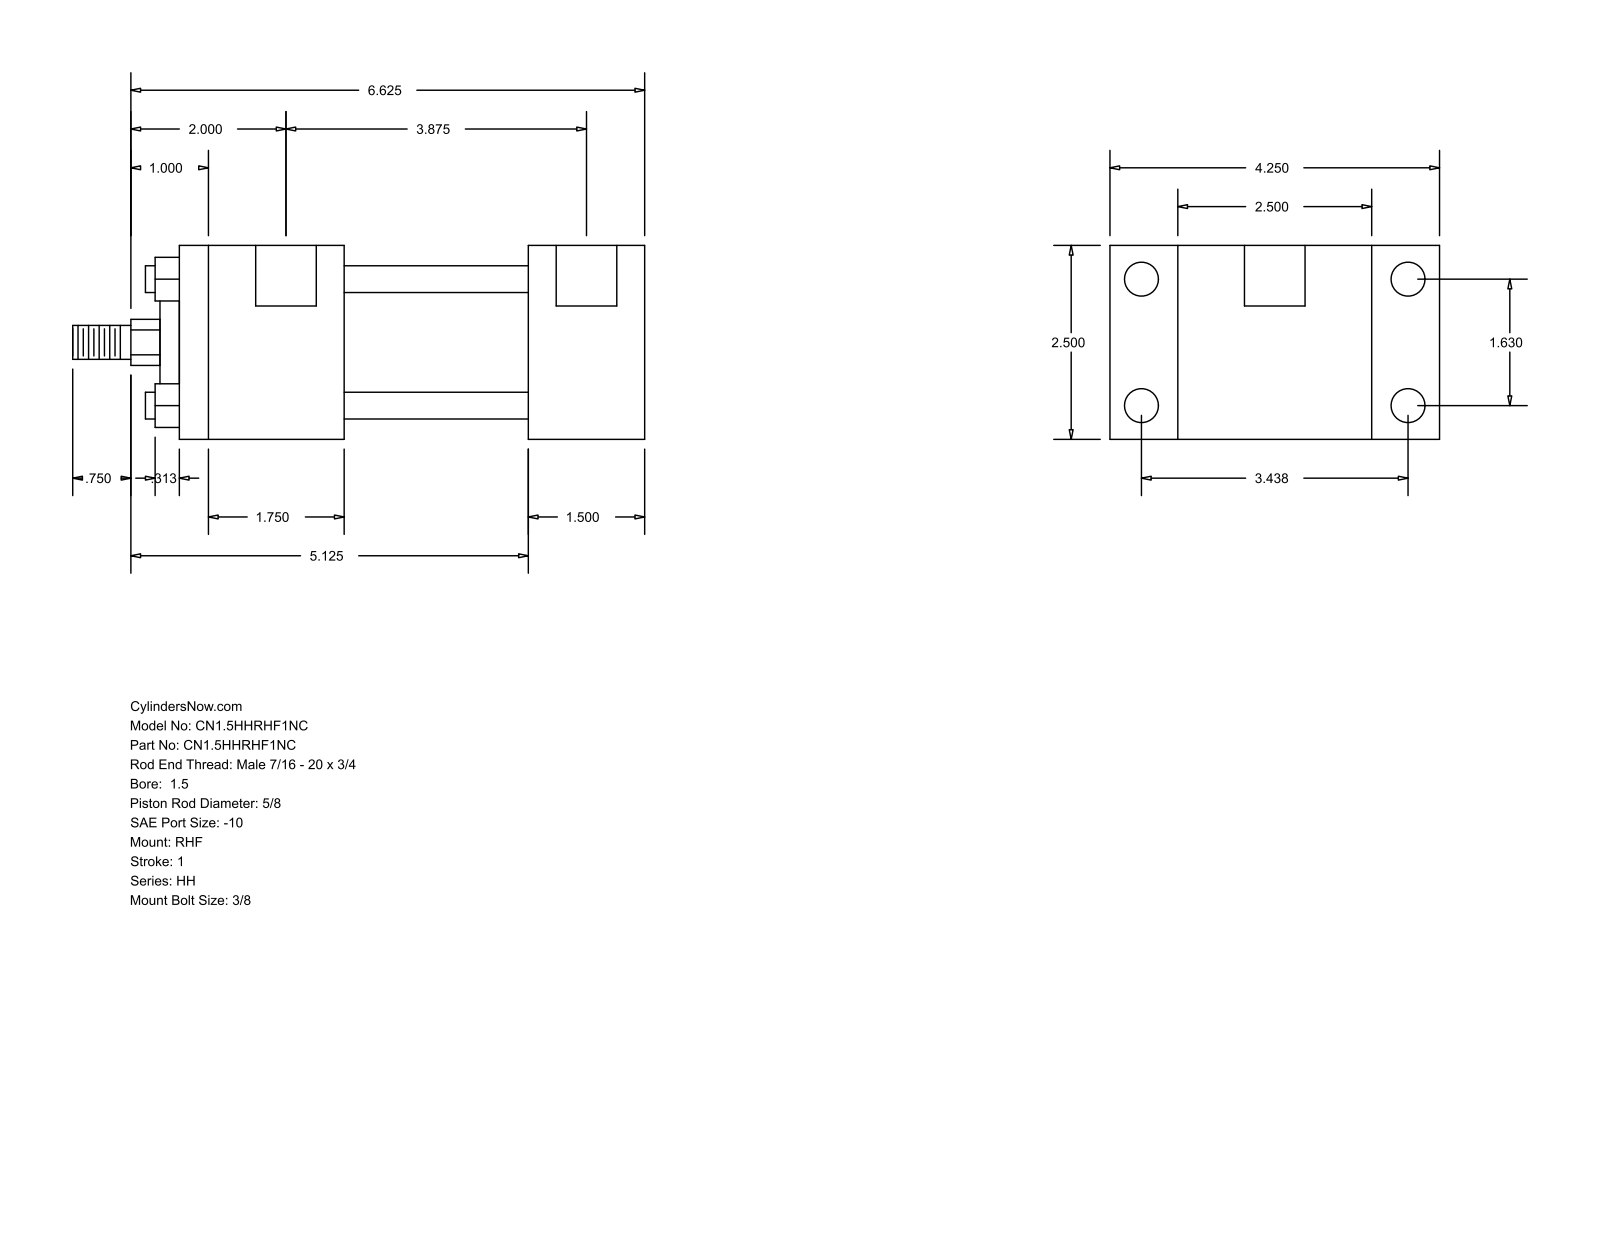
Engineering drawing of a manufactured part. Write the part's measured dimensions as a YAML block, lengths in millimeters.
part_name: "HH_RHF__0150_0.625"
step_written_by: "GSSL Pune (CONFIG_CONTROL_DESIGN)"
units: millimeters
bodies: {solids: 0, faces: 88, planar: 60, cylindrical: 28, other: 0}
overall_size: [187.32, 107.95, 63.5]
round_holes:
  - {diameter: 5.56, count: 4}
  - {diameter: 11.13, count: 4}
  - {diameter: 19.84, count: 2}
round_bosses_or_shafts:
  - {diameter: 8.76, count: 4}
  - {diameter: 44.45, count: 1}
  - {diameter: 28.57, count: 1}
  - {diameter: 15.88, count: 1}
  - {diameter: 11.11, count: 1}
partial_cylinders:
  - {radius: 7.54, count: 1}
face_to_face_distances: [63.5, 38.1, 22.23, 85.73, 114.3, 152.4, 107.96, 60.33, 53.97, 98.43]
hole_center_spacings: [1.59, 41.4, 87.32, 96.64, 100.01, 101.6, 98.42]
